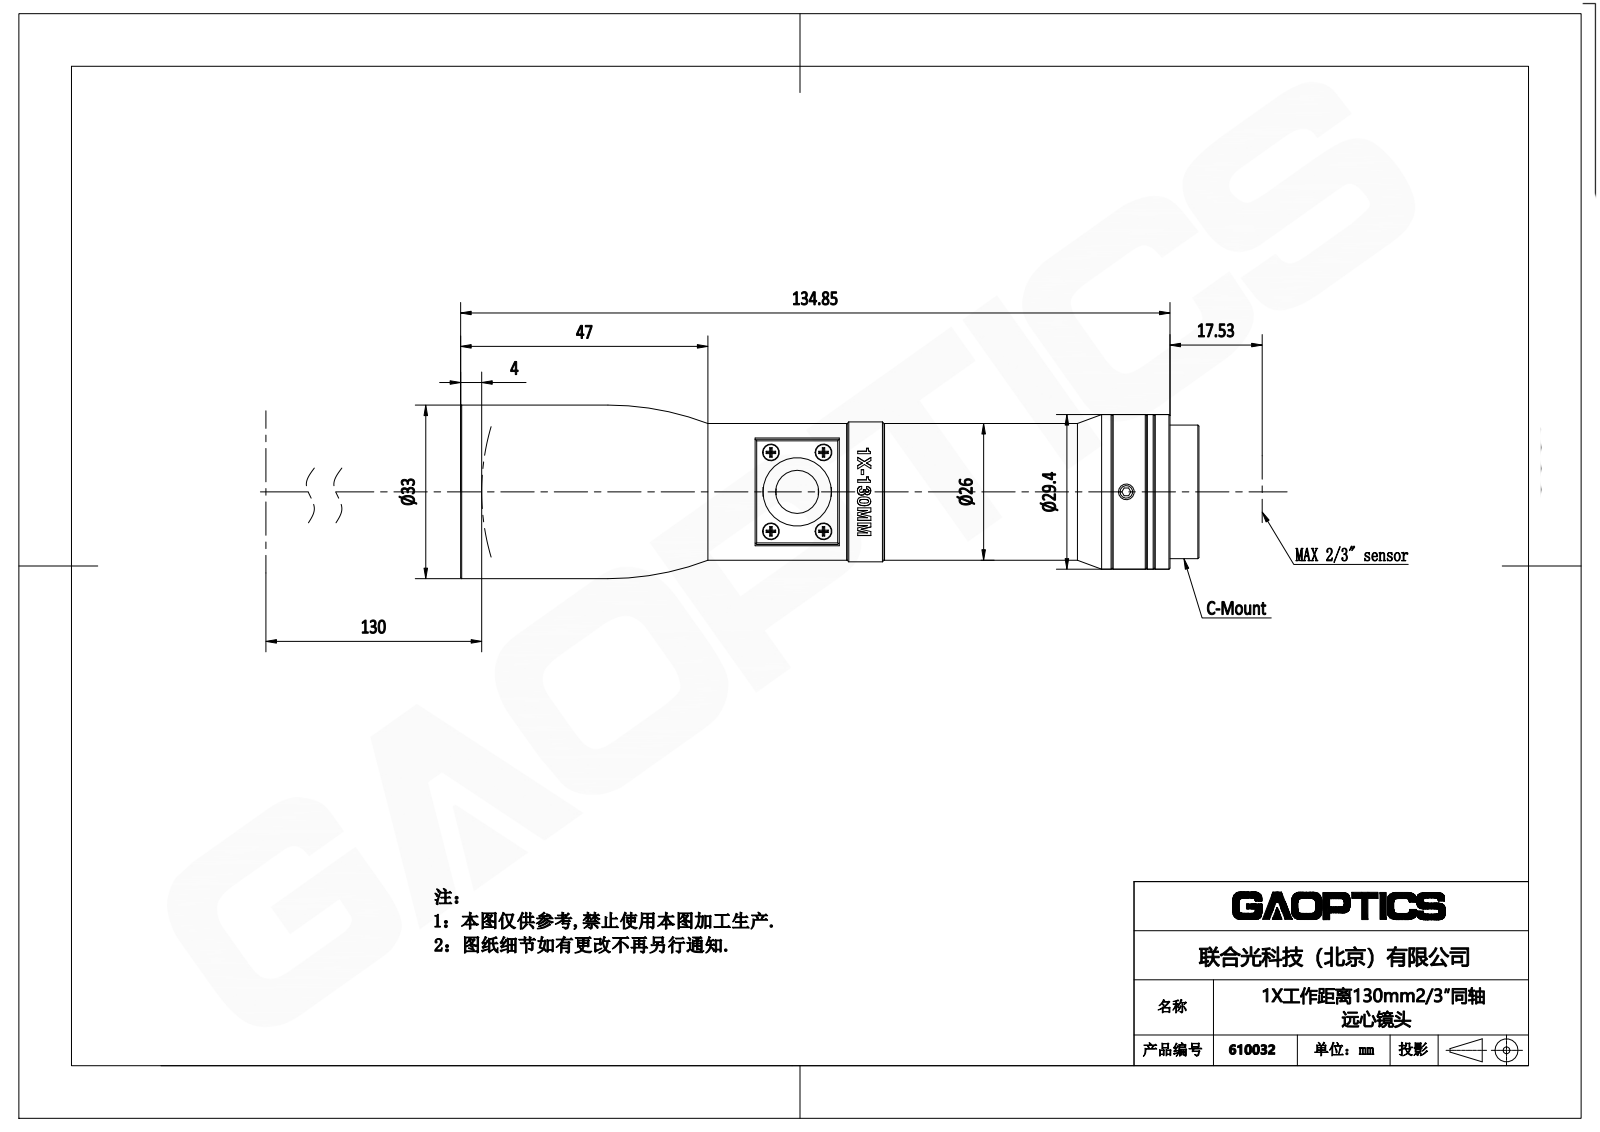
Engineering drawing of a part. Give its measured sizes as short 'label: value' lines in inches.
name: 610032
written by: SolidWorks 2016 (AUTOMOTIVE_DESIGN)
unit: in
bodies: 5 solids, 219 faces (83 planar, 82 cylindrical, 54 other)
size: 5.526 × 1.398 × 1.299
volume: 4.834 in³; area: 25.37 in²
holes: 4× ⌀0.126, 1× ⌀0.063, 1× ⌀0.315, 1× ⌀0.807, 1× ⌀0.941, 1× ⌀1.177
bosses: 4× ⌀0.11, 4× ⌀0.087, 1× ⌀1.299, 1× ⌀1.157, 1× ⌀1.047, 1× ⌀1.024, 1× ⌀1, 1× ⌀0.969
rounds: 1× R0.52
face distances: 4.943, 5.415, 0.472, 5.199, 0.256, 0.217, 0.11, 5.053, 5.309, 5.526
hole spacings: 0.335, 0.378, 0.394, 0.591, 0.71
